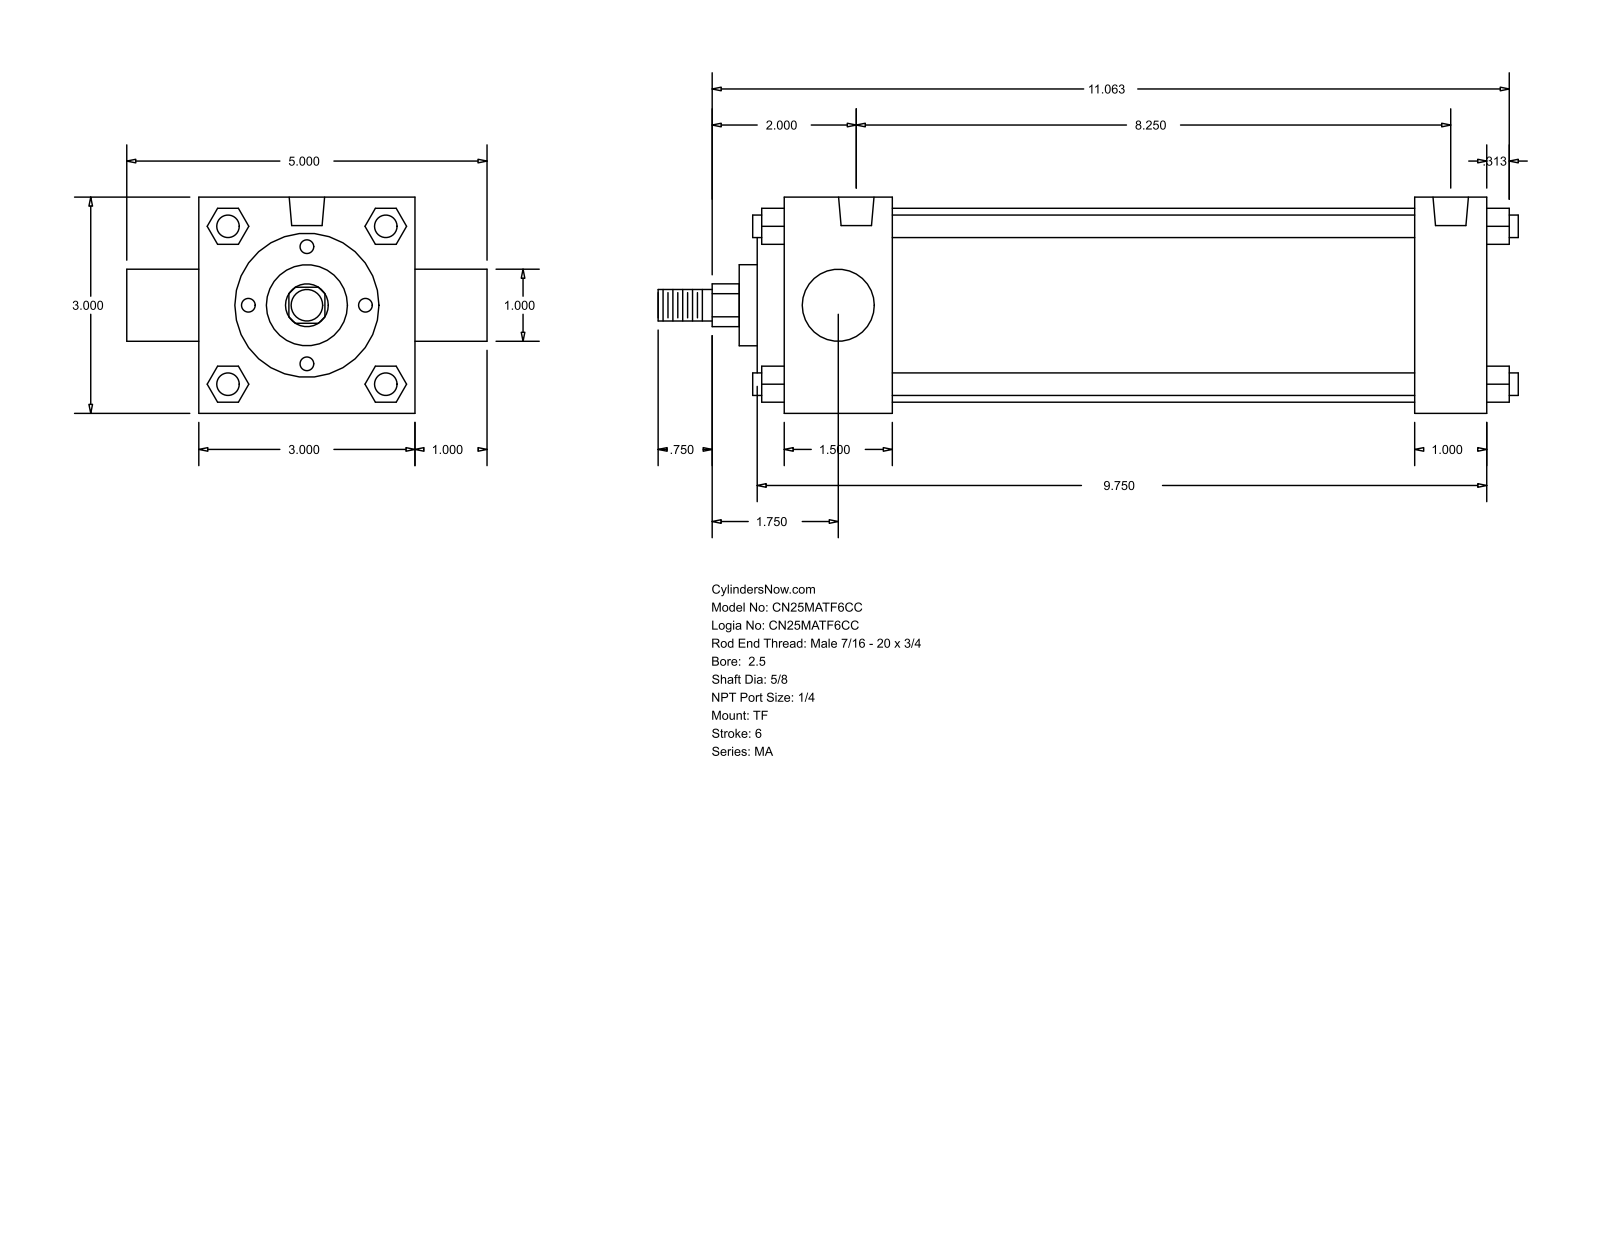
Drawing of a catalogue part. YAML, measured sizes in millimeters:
part_name: "MA_TF__0250_0.625"
step_written_by: "GSSL Pune (CONFIG_CONTROL_DESIGN)"
units: millimeters
bodies: {solids: 0, faces: 122, planar: 93, cylindrical: 29, other: 0}
overall_size: [303.21, 127, 76.2]
round_holes:
  - {diameter: 7.94, count: 3}
  - {diameter: 12.49, count: 2}
round_bosses_or_shafts:
  - {diameter: 7.94, count: 4}
  - {diameter: 68.33, count: 1}
  - {diameter: 50.8, count: 1}
  - {diameter: 28.57, count: 1}
  - {diameter: 25.4, count: 1}
  - {diameter: 15.88, count: 1}
  - {diameter: 11.11, count: 1}
partial_cylinders:
  - {radius: 7.54, count: 1}
face_to_face_distances: [76.2, 247.65, 25.4, 38.1, 222.25, 184.15, 209.55, 12.7, 9.52, 47.62]
hole_center_spacings: [209.55]
